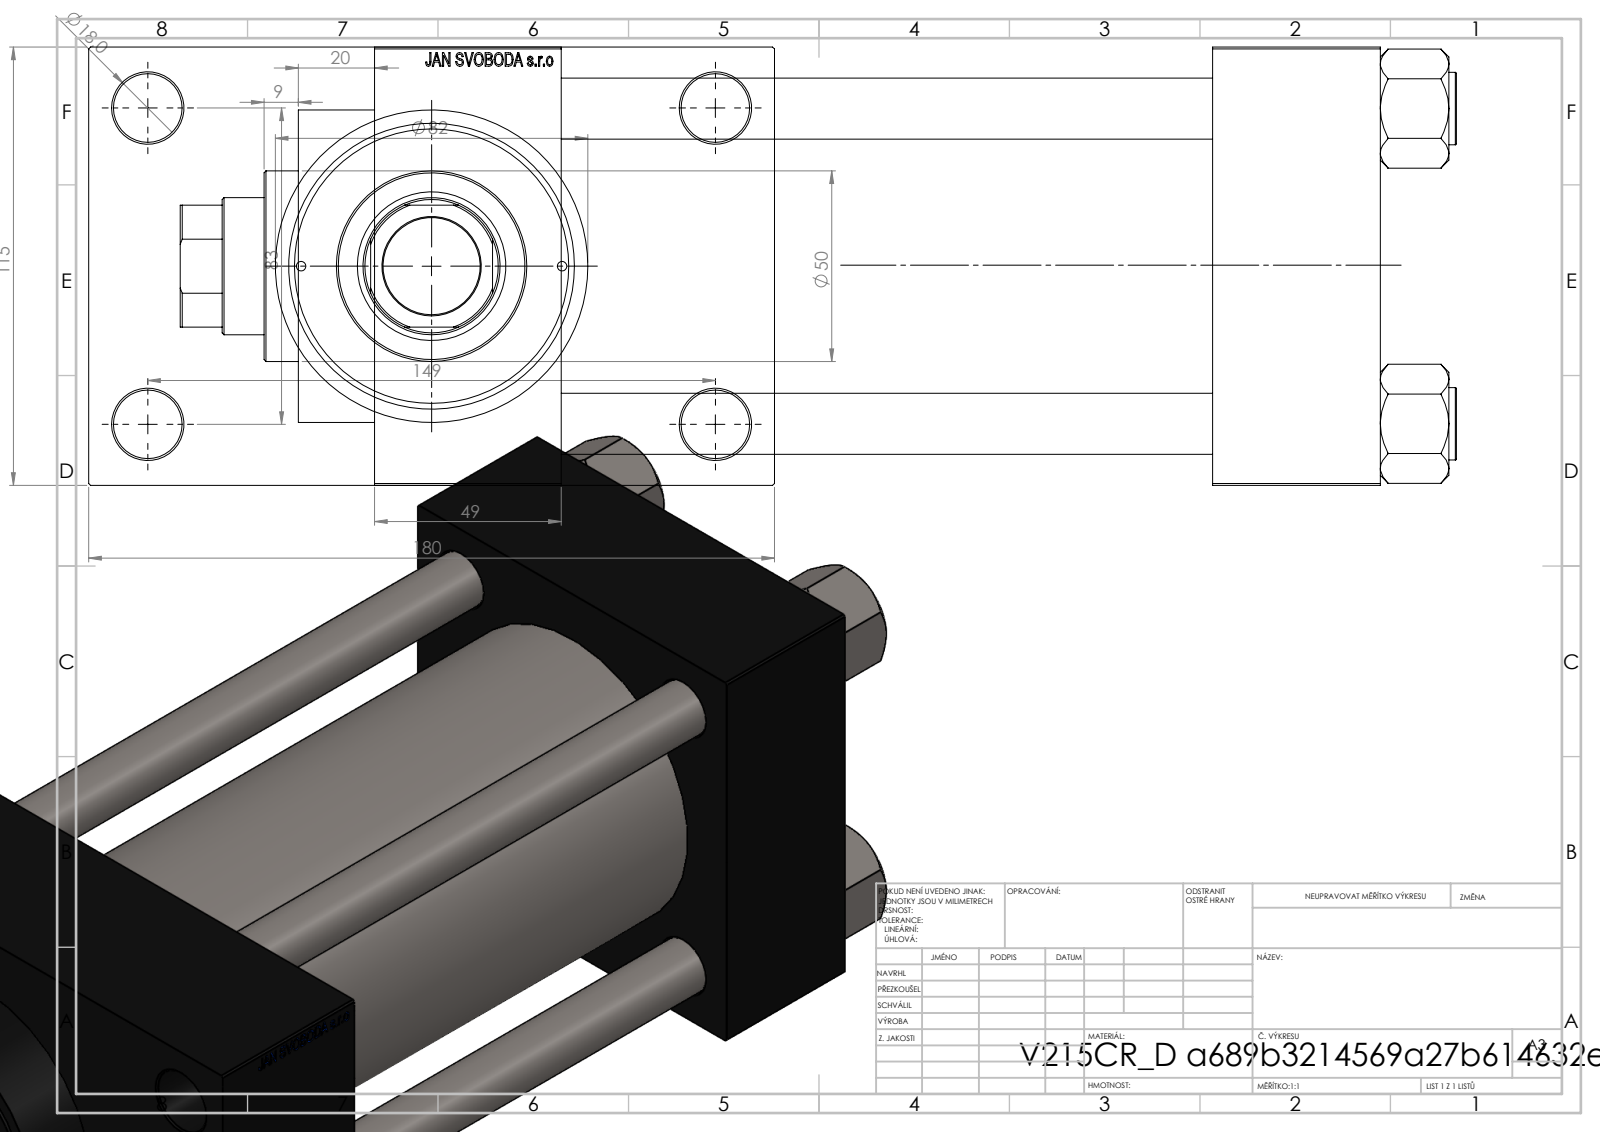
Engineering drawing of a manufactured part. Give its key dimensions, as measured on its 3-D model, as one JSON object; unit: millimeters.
{"part_name": "NUT_M5_D; V215_VC_A; V215CR_VCP_D; V215CR_D_TYCINKA (+1 more)", "step_written_by": "SolidWorks 2019 (CONFIG_CONTROL_DESIGN)", "units": "millimeters", "bodies": {"solids": 11, "faces": 1159, "planar": 547, "cylindrical": 92, "other": 520}, "overall_size": [335, 180, 115], "volume_mm3": 2253000, "surface_area_mm2": 384222, "round_holes": [[16, 4], [18, 4], [2.5, 2], [7, 2], [26.44, 2], [35, 2], [25.5, 1], [36, 1], [39, 1], [61, 1], [72, 1], [80, 1]], "round_bosses_or_shafts": [[19, 4], [86, 1], [82, 1], [50, 1]], "partial_cylinders_radius": [[17.5, 1]], "face_to_face_distances": [115, 171, 220, 49, 44, 215, 264, 32.5, 147.5, 180], "hole_center_spacings": [33.15, 41.96, 57.81, 58.48, 82.7, 85.28, 86.17, 89.24]}
